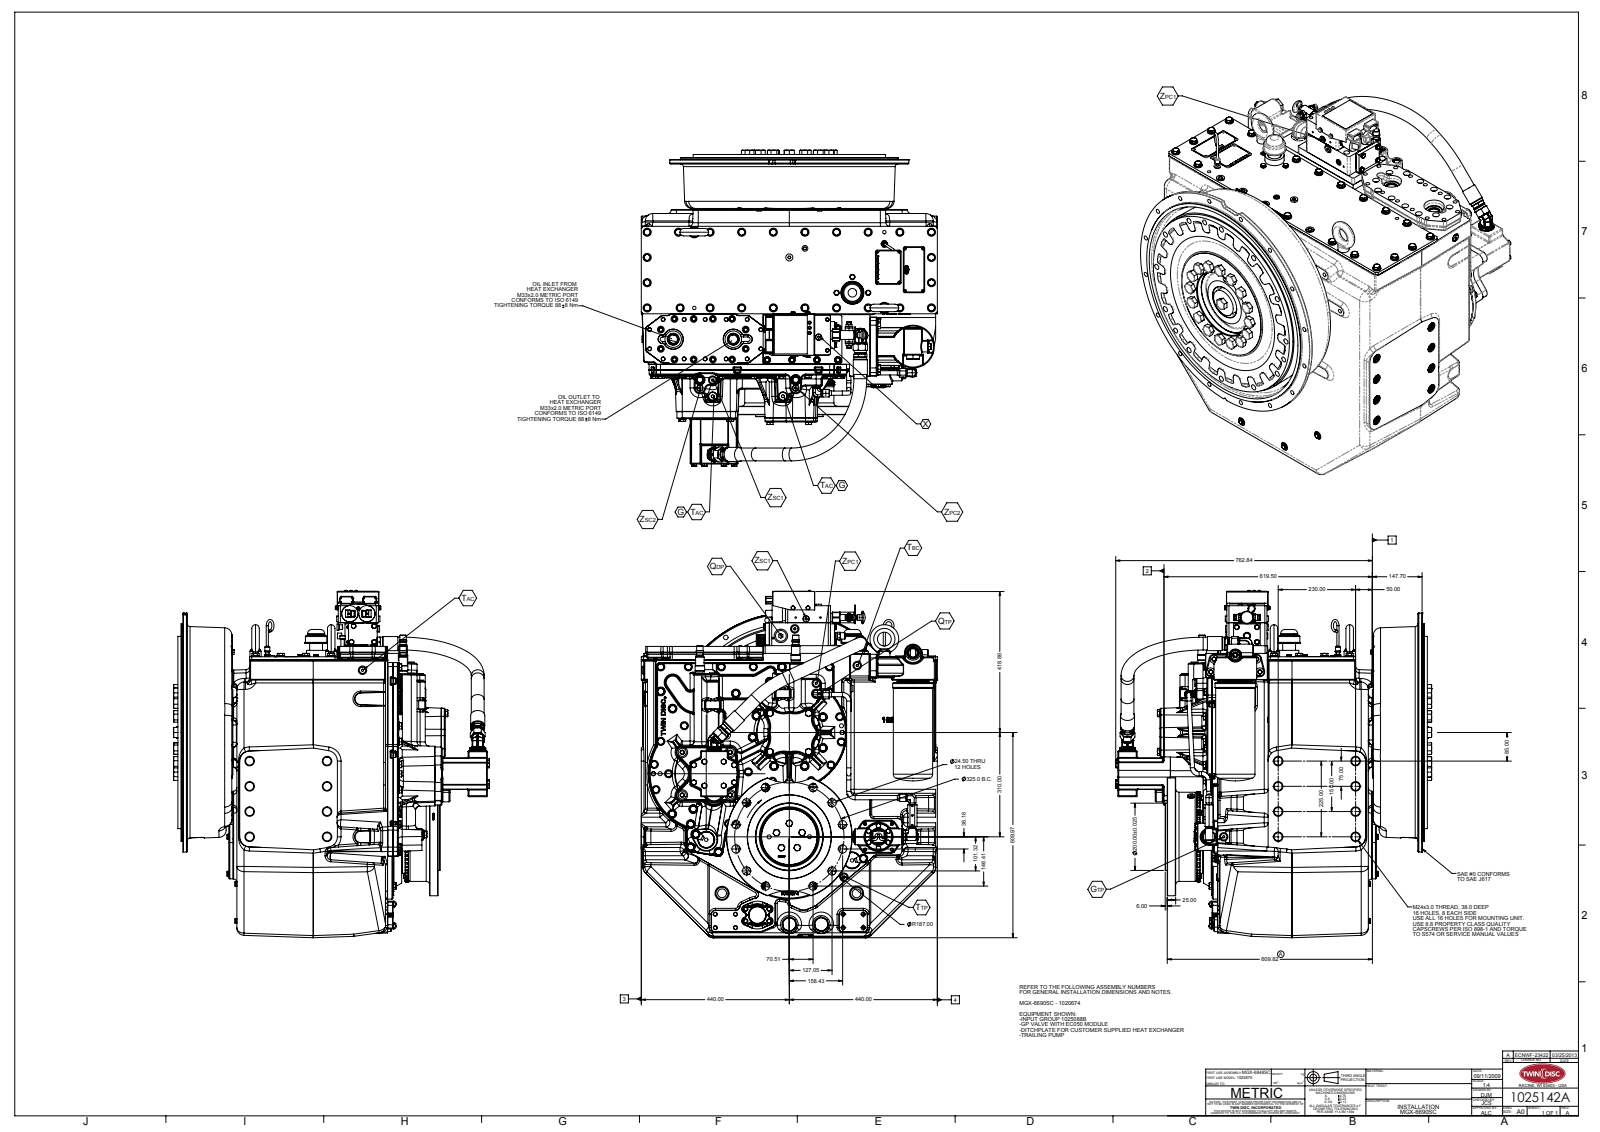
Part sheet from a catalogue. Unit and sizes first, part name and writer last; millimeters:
Units: millimetres
Overall size (bounding box): 1032.84 × 938.94 × 887.13
Round holes (diameter × count): ⌀4.5 ×232, ⌀12 ×32, ⌀20 ×18, ⌀13.5 ×16, ⌀17.02 ×12, ⌀24.5 ×12, ⌀10 ×10, ⌀25 ×10, ⌀26 ×9, ⌀28.24 ×8, ⌀10.2 ×6, ⌀16 ×3
Round bosses / shafts (diameter × count): ⌀24 ×71, ⌀18 ×36, ⌀19 ×11, ⌀15.32 ×6, ⌀12.5 ×6, ⌀12.7 ×5, ⌀38.1 ×4, ⌀17 ×4
Partial cylindrical surfaces — rounded edges, fillets, slot ends (radius × count): R3 ×191, R6 ×106, R43.44 ×95, R12 ×90, R2.54 ×50, R50 ×50, R10 ×48, R3.05 ×32
Main face-to-face distances: 464.5, 0.5, 465, 15, 480, 17, 16.5, 448, 10.09, 479.5
Hole centre spacings: 162.5, 72.32, 75, 241.92, 132.95, 202.64, 40, 60
Bodies: 0 solids, 5485 faces (2060 planar, 1728 cylindrical, 1697 other)
Part name (STEP PRODUCT): 1025142A
STEP written by: SolidWorks 2015 (AUTOMOTIVE_DESIGN)
